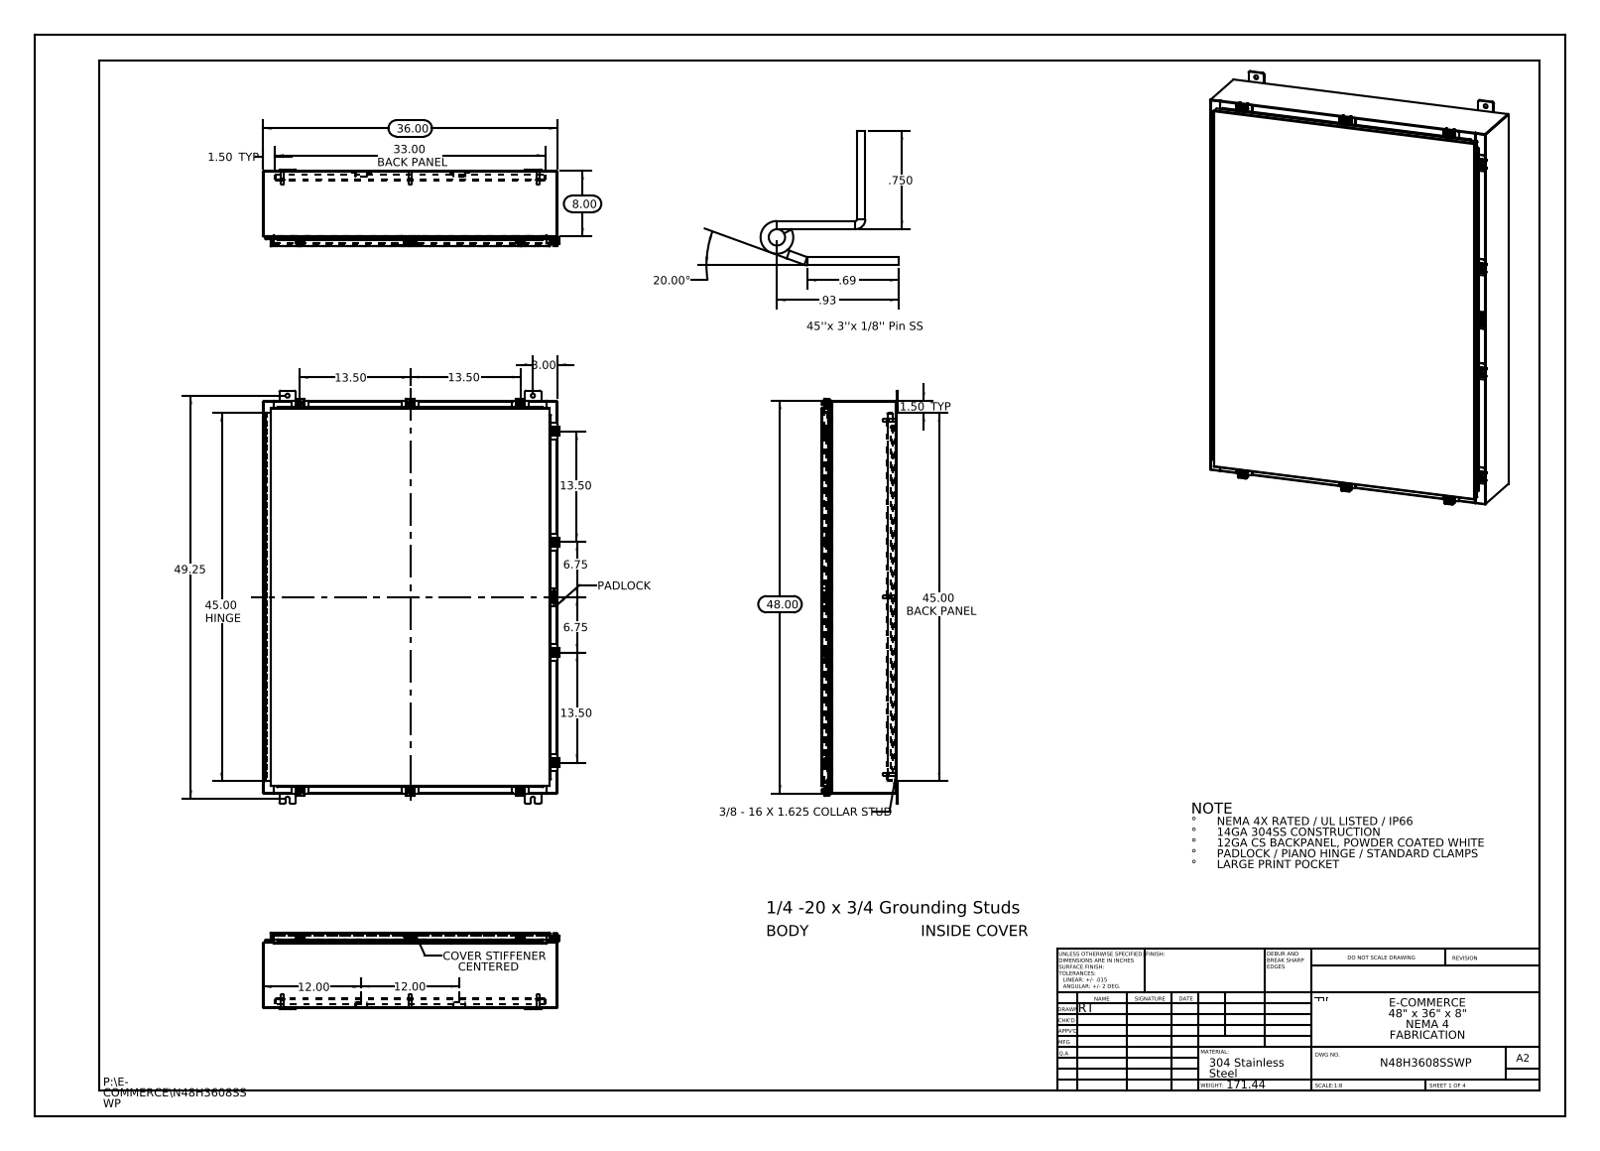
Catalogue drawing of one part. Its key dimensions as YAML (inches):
part_name: "N48H3608SSWP 22104005_DEFAULT; N48H3608SSWP Door Stiffener; N48H3608SSWP Padlock Staple; N48H3608SSWP Padlock Hasp (+8 more)"
step_written_by: "SolidWorks 2013 (CONFIG_CONTROL_DESIGN)"
units: inches
bodies: {solids: 74, faces: 2999, planar: 1562, cylindrical: 1269, other: 168}
overall_size: [50.5, 36.211, 9.389]
volume: 600.8
surface_area: 14917
round_holes:
  - {diameter: 0.5, count: 12}
  - {diameter: 0.213, count: 10}
  - {diameter: 0.26, count: 10}
  - {diameter: 0.25, count: 6}
  - {diameter: 0.125, count: 2}
  - {diameter: 0.125, count: 1}
round_bosses_or_shafts:
  - {diameter: 0.25, count: 11}
  - {diameter: 0.5, count: 10}
  - {diameter: 0.399, count: 10}
  - {diameter: 0.625, count: 8}
  - {diameter: 0.375, count: 8}
  - {diameter: 0.33, count: 8}
partial_cylinders:
  - {radius: 0.06, count: 46}
  - {radius: 0.013, count: 39}
  - {radius: 0.088, count: 33}
  - {radius: 0.19, count: 24}
  - {radius: 0.12, count: 20}
  - {radius: 0.141, count: 20}
  - {radius: 0.05, count: 15}
  - {radius: 0.08, count: 14}
face_to_face_distances: [0.075, 9.126, 9.051, 0.104, 9.201, 1, 8.126, 1.075, 8.051, 1.179]
hole_center_spacings: [13.5, 13.663, 20, 20.123, 21.625, 23.82, 27, 38.003]
